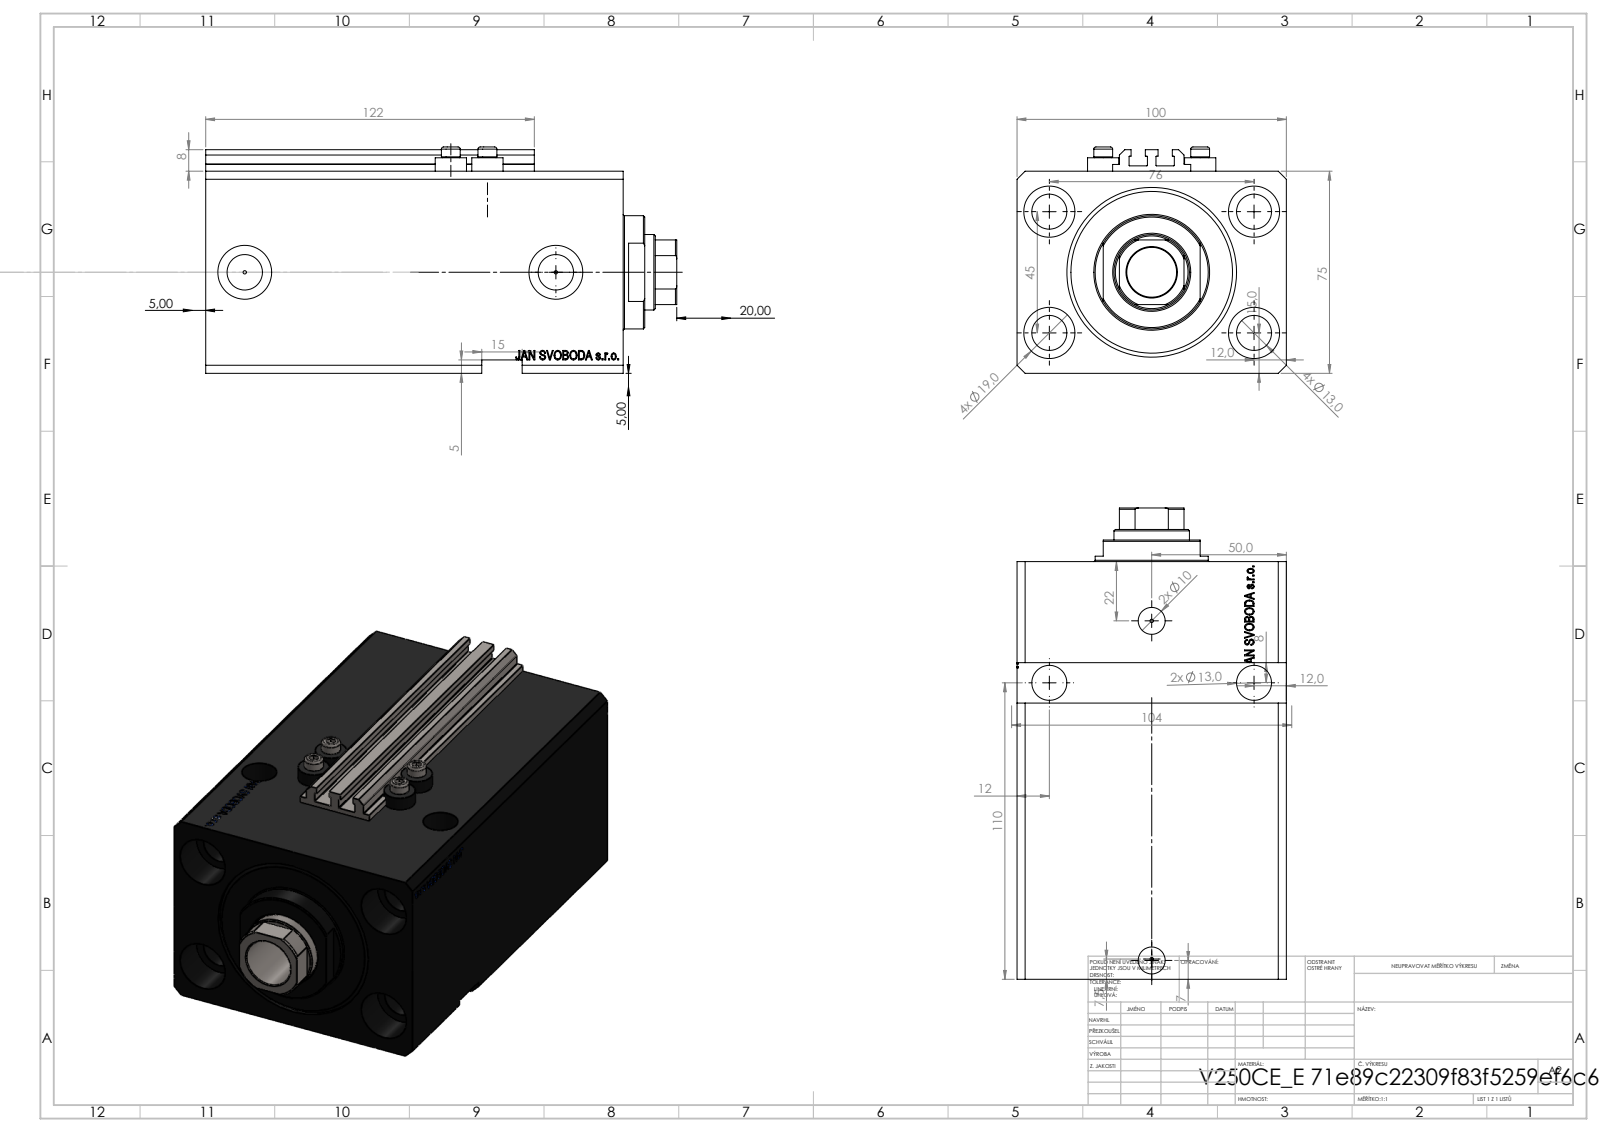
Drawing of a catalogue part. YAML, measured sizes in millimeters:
part_name: "V250CE_C_VCP; V250CE_E_Body; V250CE_VC_E; ALLEN BOLT V250CE"
step_written_by: "SolidWorks 2019 (CONFIG_CONTROL_DESIGN)"
units: millimeters
bodies: {solids: 8, faces: 1108, planar: 535, cylindrical: 146, other: 427}
overall_size: [175, 100, 84]
volume: 940698
surface_area: 175915
round_holes:
  - {diameter: 13, count: 8}
  - {diameter: 1.25, count: 4}
  - {diameter: 4, count: 4}
  - {diameter: 19, count: 4}
  - {diameter: 10, count: 2}
  - {diameter: 13.16, count: 2}
  - {diameter: 20, count: 2}
  - {diameter: 18.5, count: 1}
  - {diameter: 28, count: 1}
  - {diameter: 50, count: 1}
  - {diameter: 63, count: 1}
round_bosses_or_shafts:
  - {diameter: 11.6, count: 4}
  - {diameter: 7, count: 4}
  - {diameter: 42, count: 1}
partial_cylinders:
  - {radius: 0.2, count: 10}
  - {radius: 13.5, count: 1}
face_to_face_distances: [75, 100, 155, 20, 11.9, 143.1, 135, 123.1, 8, 80]
hole_center_spacings: [44.16, 76, 13.6, 20.72, 27.59, 33.62, 36, 38.48]
